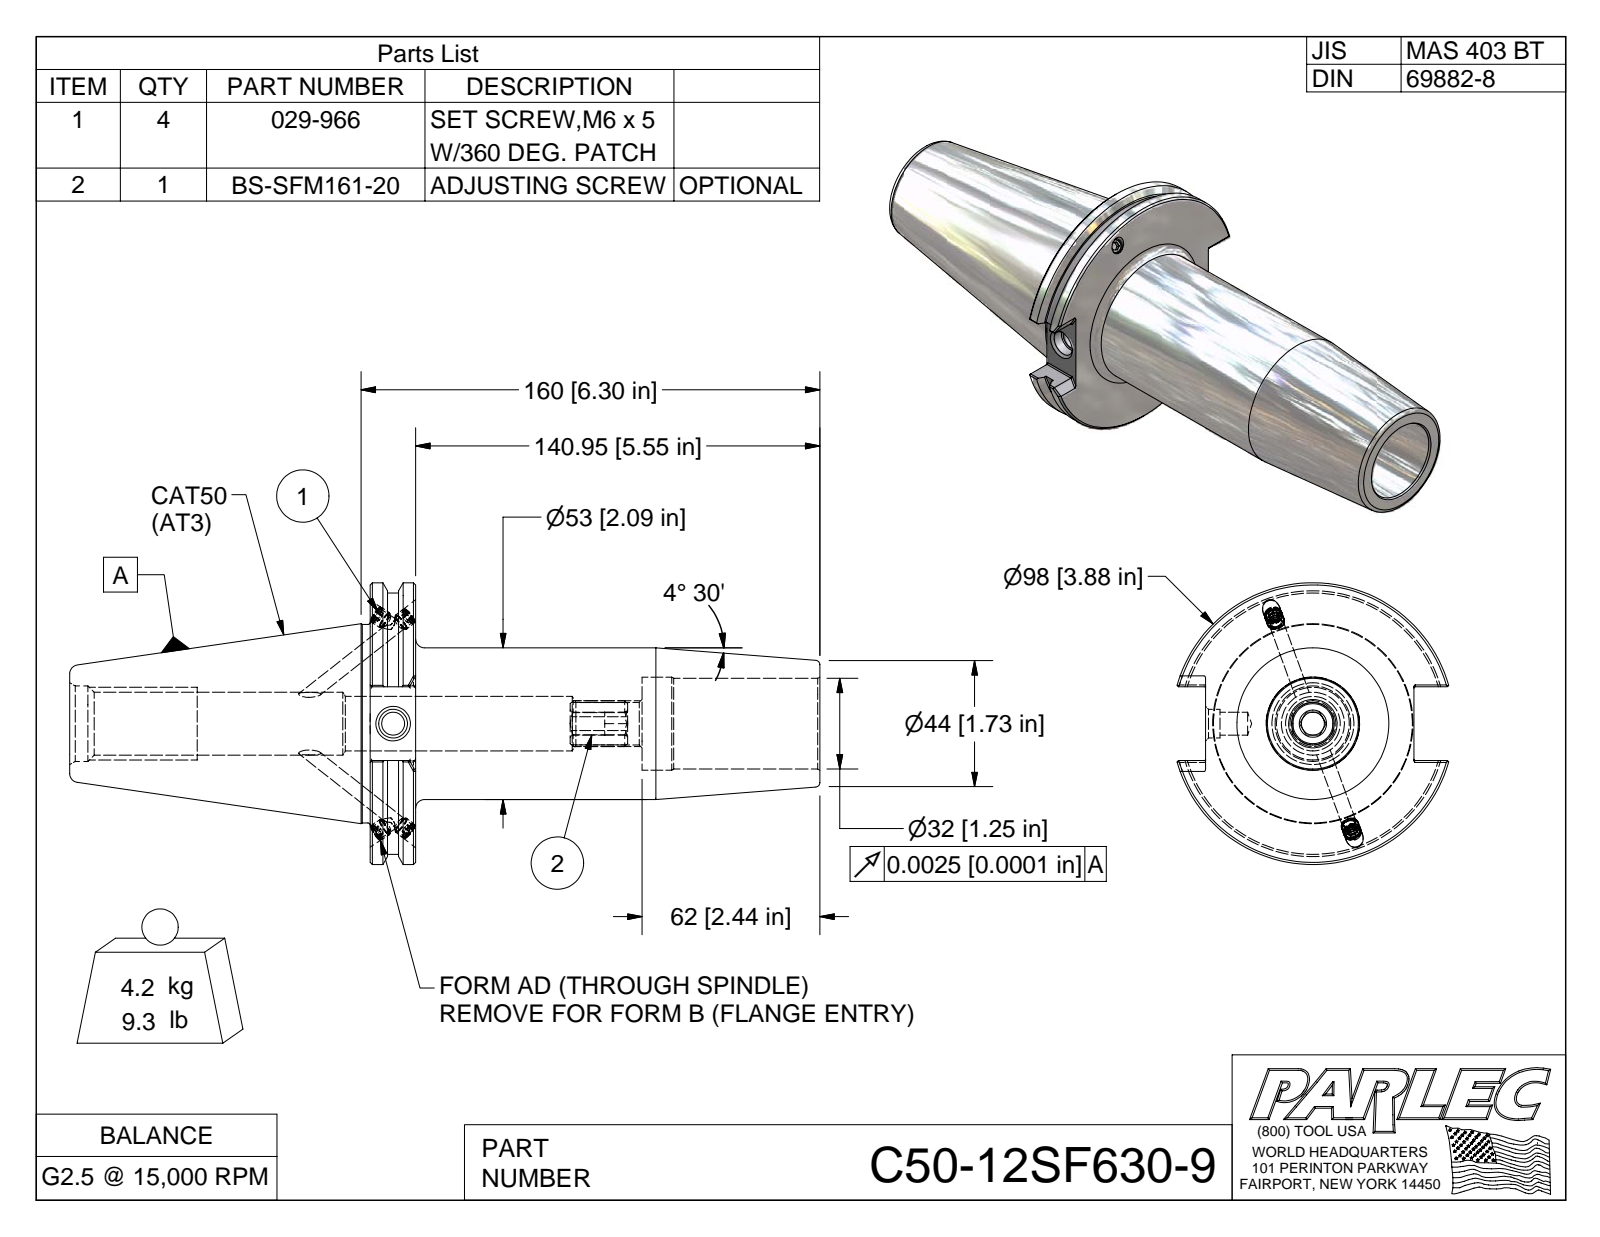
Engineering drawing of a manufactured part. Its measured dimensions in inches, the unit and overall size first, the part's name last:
Units: inches
Overall size (bounding box): 10.299 × 3.875 × 3.729
Round holes (diameter × count): ⌀0.197 ×4, ⌀0.24 ×4, ⌀1.248 ×1, ⌀1.278 ×1
Round bosses / shafts (diameter × count): ⌀0.244 ×4, ⌀0.236 ×4, ⌀3.875 ×1, ⌀3.594 ×1, ⌀2.73 ×1, ⌀2.087 ×1
Partial cylindrical surfaces — rounded edges, fillets, slot ends (radius × count): R0.02 ×12, R0.315 ×1
Main face-to-face distances: 0.625, 3.733, 3.108, 6.174, 5.549, 2.441, 4.125, 4.75, 7.858, 10.299
Volume: 33.1 in³ · Surface area: 124.4 in²
Bodies: 6 solids, 186 faces (87 planar, 44 cylindrical, 55 other)
Part name (STEP PRODUCT): C50-12SF630-9; C50BC-12SF630-9-1; BS-SFM161-20; 029-966
STEP written by: Autodesk Inventor 2009 (AUTOMOTIVE_DESIGN)
